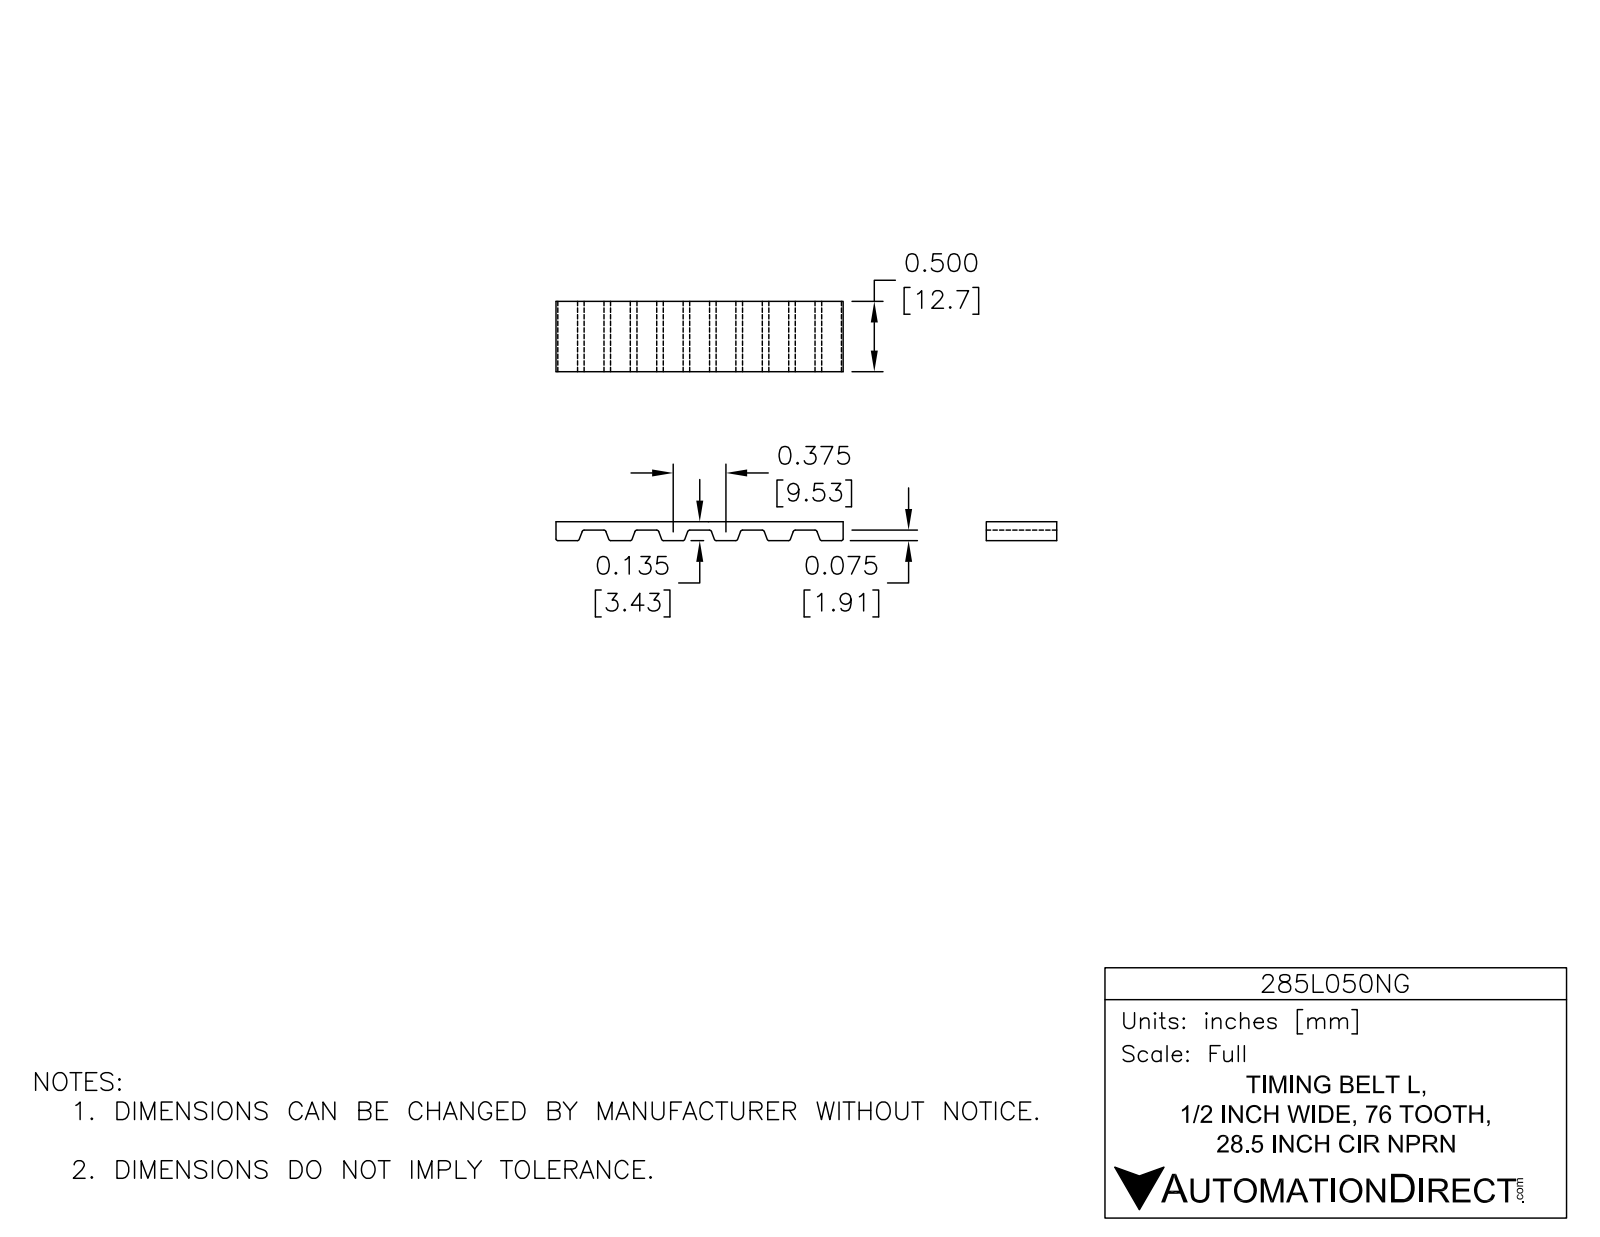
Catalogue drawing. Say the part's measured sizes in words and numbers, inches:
The part is named "285L050NG". Its 3-D file was written by "SolidWorks 2014 (AUTOMOTIVE_DESIGN)". It is 1 solid with 623 faces: 281 planar, 342 cylindrical and 0 other. Overall it measures 12.538 by 3 by 0.5 inches. Its volume is 1.288 cubic inches and its surface area 36.84 square inches. Partial cylindrical surfaces (rounded edges, fillets, slot ends): 300 of radius 0.02, 2 of radius 1.435, 2 of radius 1.5. The main face-to-face distances are 0.065, 2.935, 3, 0.5, 2.87, 2.795, 0.14, 2.86, 0.075, 2.72.
